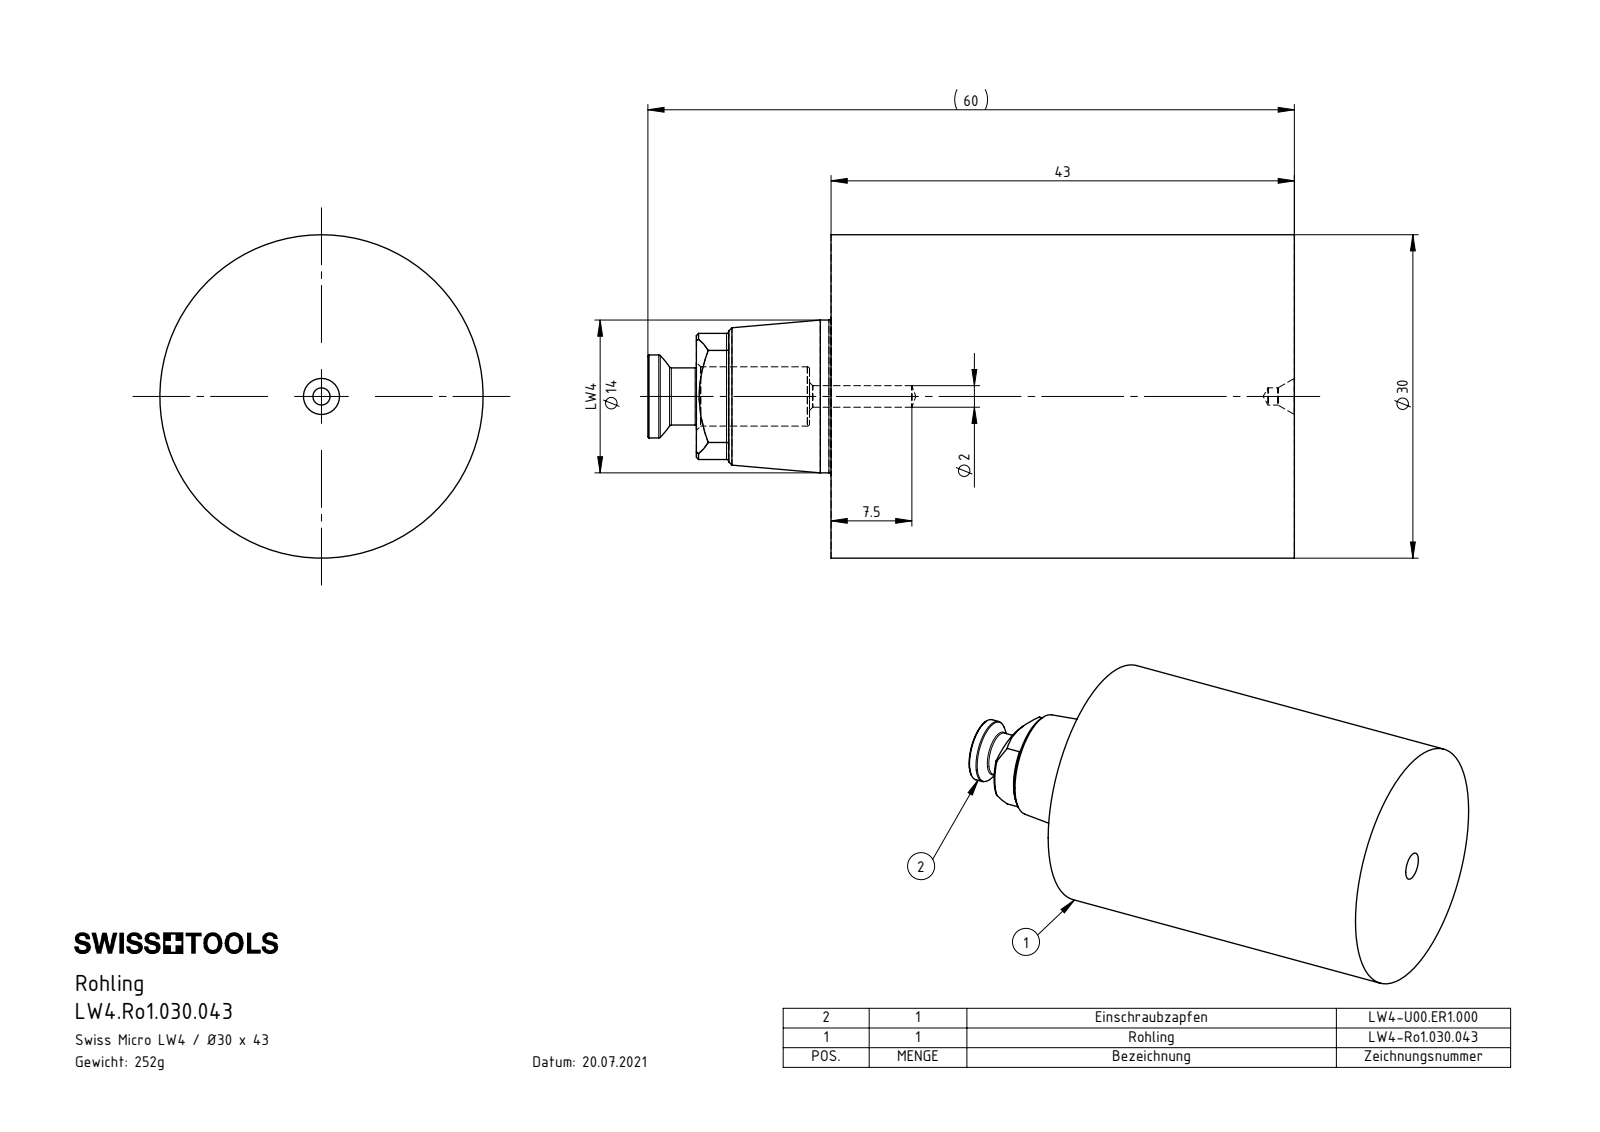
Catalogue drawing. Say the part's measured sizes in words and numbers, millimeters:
The part is named "LW4-Ro1.030.043_A; LW4.Ro1.030.043; LW4-U00.ER1.000_B". Its 3-D file was written by "SolidWorks 2017 (AUTOMOTIVE_DESIGN)". It is 2 solids with 56 faces: 15 planar, 14 cylindrical and 27 other. Overall it measures 60 by 30 by 30 millimeters. Its volume is 32 061 cubic millimeters and its surface area 6 628 square millimeters. Round holes: 1 of diameter 1.6, 1 of diameter 2, 1 of diameter 2.5, 1 of diameter 5.5. Round bosses or shafts: 1 of diameter 30, 1 of diameter 14.17, 1 of diameter 7.7, 1 of diameter 6, 1 of diameter 5.3, 1 of diameter 5. Partial cylindrical surfaces (rounded edges, fillets, slot ends): 2 of radius 0.2, 1 of radius 5.85. The main face-to-face distances are 43, 7.5, 2, 12.5, 55.5, 4.5, 17, 60, 15, 10.5.
